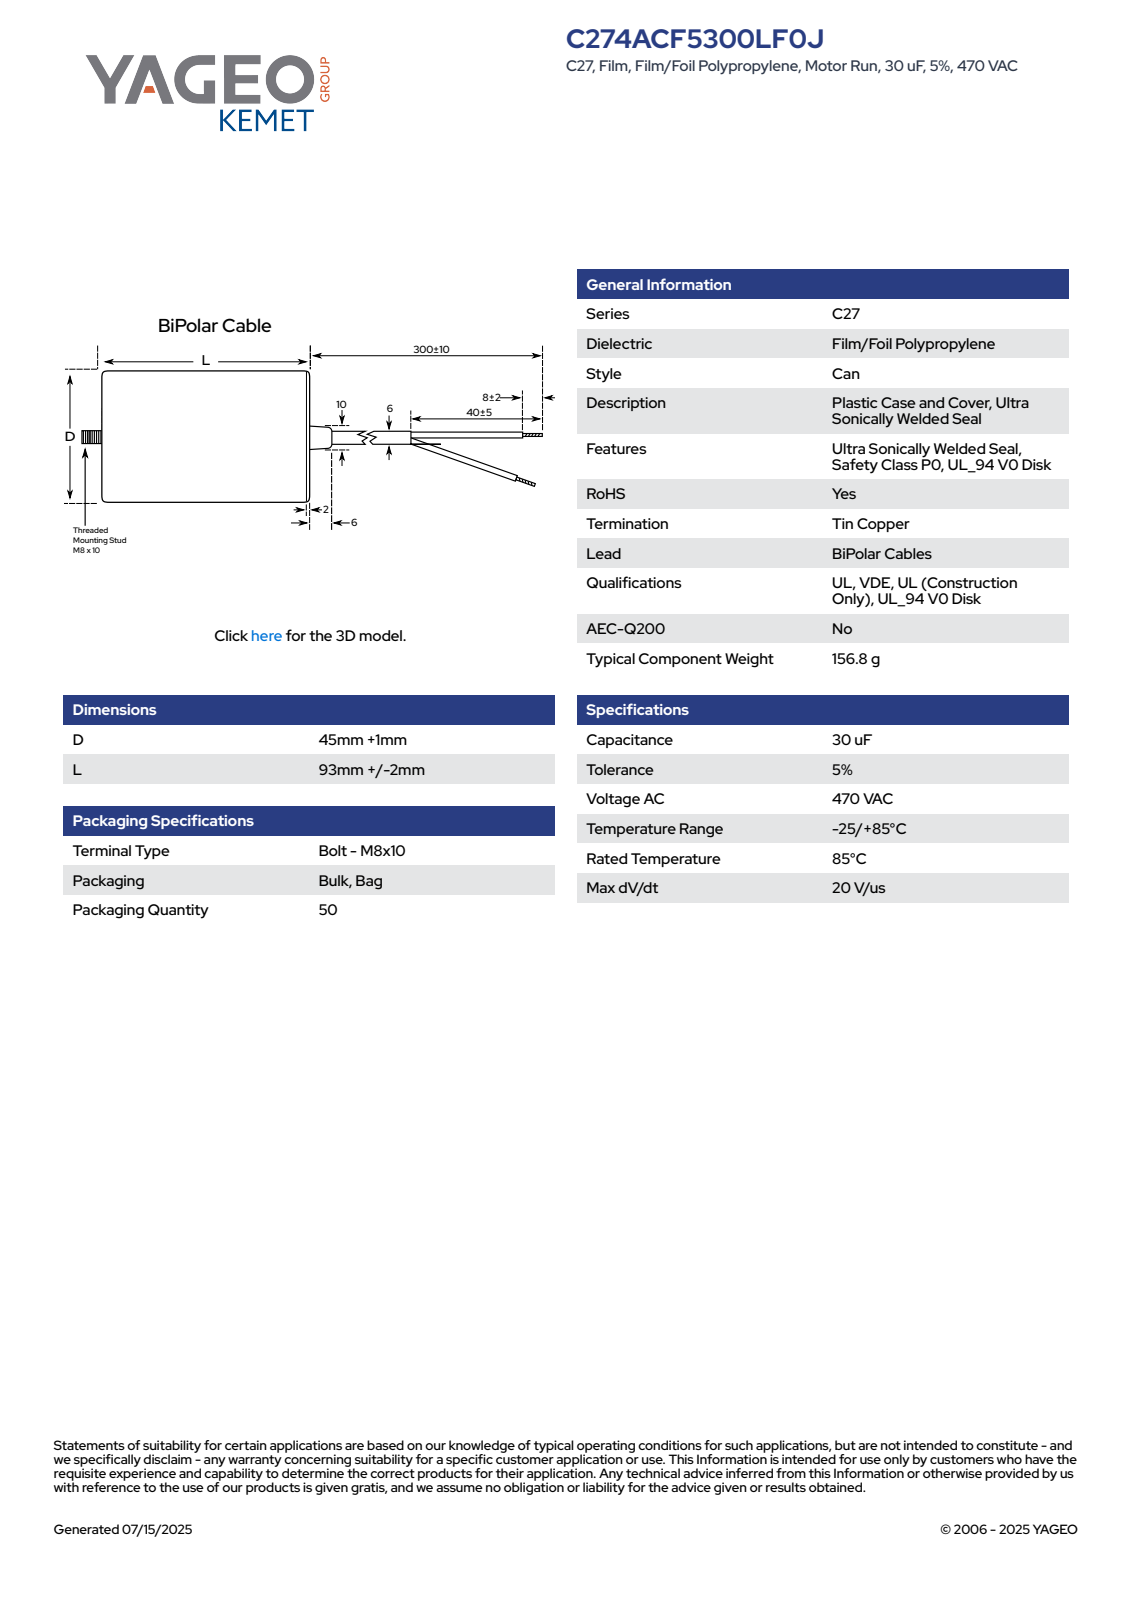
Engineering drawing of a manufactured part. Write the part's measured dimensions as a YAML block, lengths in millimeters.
part_name: "CFM_KC27BI_45X93_D46L95"
step_written_by: "SolidWorks 2014 (AUTOMOTIVE_DESIGN)"
units: millimeters
bodies: {solids: 2, faces: 82, planar: 28, cylindrical: 15, other: 39}
overall_size: [111, 46.01, 46]
volume: 155932
surface_area: 17738
round_holes:
  - {diameter: 42, count: 1}
round_bosses_or_shafts:
  - {diameter: 46, count: 1}
  - {diameter: 8, count: 1}
partial_cylinders:
  - {radius: 23.01, count: 1}
face_to_face_distances: [93, 95, 2, 10, 103, 105, 111, 101, 8, 6]
